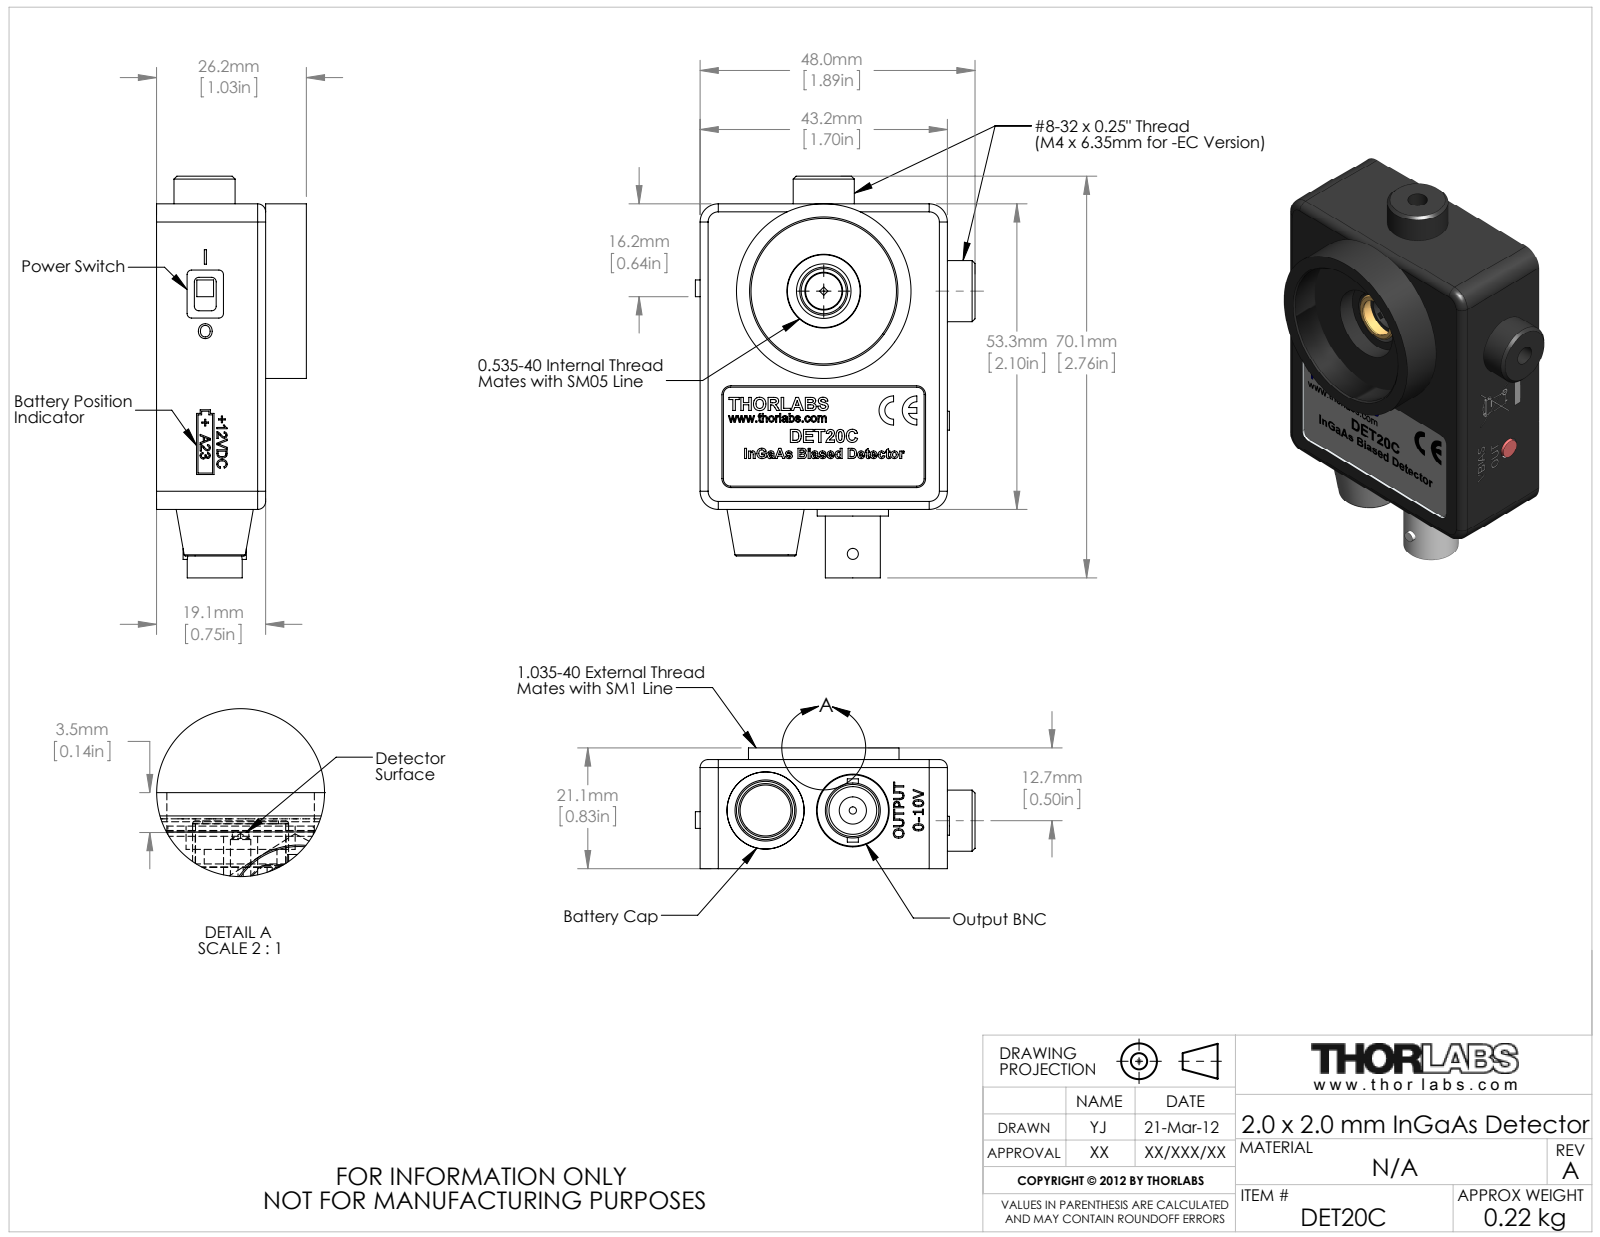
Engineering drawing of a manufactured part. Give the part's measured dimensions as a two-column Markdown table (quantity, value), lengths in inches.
| quantity | value |
| --- | --- |
| part name | 23157-E0W |
| STEP written by | SolidWorks 2011 (AUTOMOTIVE_DESIGN) |
| units | inches |
| bodies | 14 solids, 1901 faces (1039 planar, 272 cylindrical, 590 other) |
| overall size | 2.761 × 1.922 × 1.03 |
| volume | 1.365 in³ |
| surface area | 40.72 in² |
| round holes (diameter × count) | 0.028 × 7, 0.07 × 7, 0.096 × 7, 0.125 × 4, 0.2 × 4, 0.15 × 3, 0.136 × 2, 0.23 × 2, 0.017 × 1, 0.05 × 1, 0.05 × 1, 0.052 × 1 |
| round bosses / shafts (diameter × count) | 0.039 × 4, 0.018 × 3, 0.42 × 2, 0.236 × 2, 1.2 × 1, 1.035 × 1, 0.5 × 1, 0.49 × 1 |
| partial cylindrical surfaces (radius × count) | 0.125 × 26, 0.031 × 10, 0.095 × 8, 0.004 × 6, 0.02 × 6, 0.016 × 4, 0.05 × 4, 0.055 × 4 |
| main face-to-face distances | 0.063, 0.452, 0.1, 0.515, 0.07, 0.05, 0.165, 0.02, 0.228, 0.68 |
| hole center spacings | 0.05, 0.112, 0.1, 0.071, 0.15, 0.141, 0.403, 0.689 |
